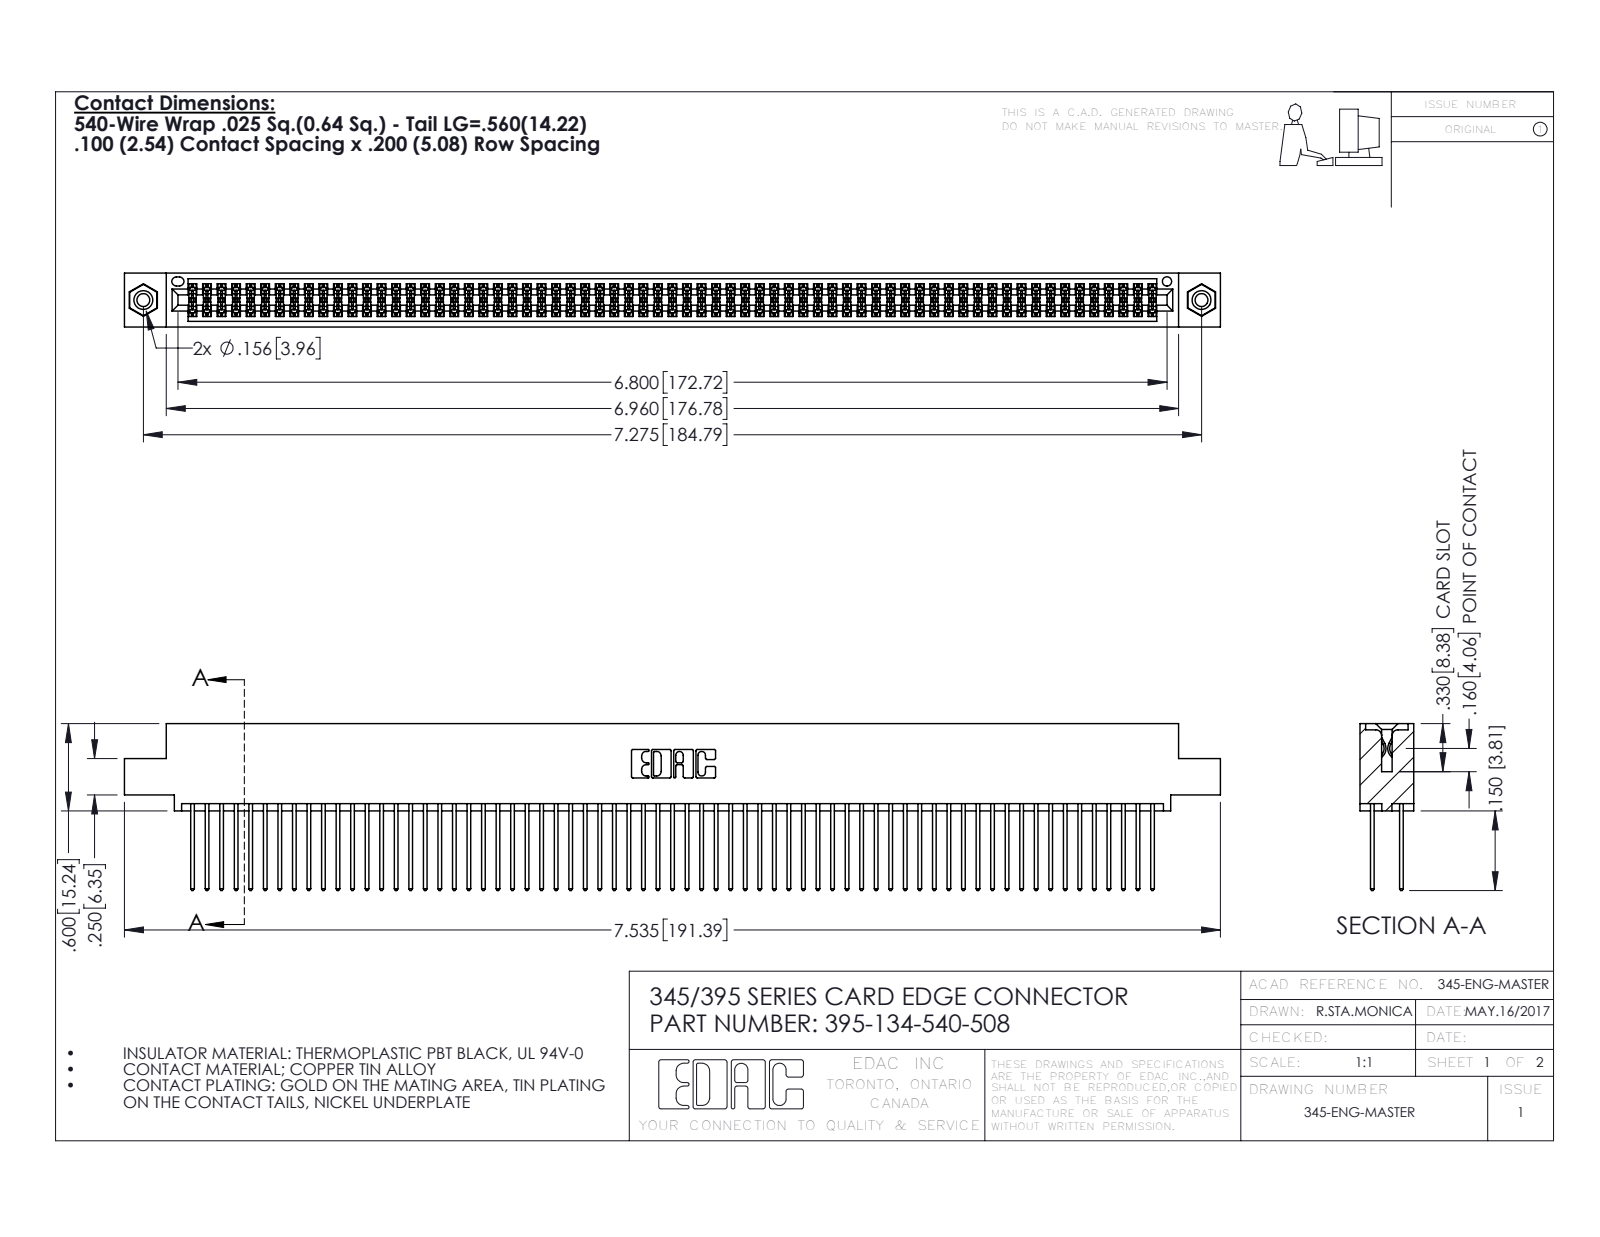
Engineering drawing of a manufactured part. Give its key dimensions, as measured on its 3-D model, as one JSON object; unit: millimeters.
{"part_name": "345 Part_0.110 Offset - 0.156 Dia-TI; 395-134-540-508; 345-292-001_345-293-140; 345-250-001_345-250-003-102", "step_written_by": "SolidWorks 2016 (CONFIG_CONTROL_DESIGN)", "units": "millimeters", "bodies": {"solids": 137, "faces": 6890, "planar": 4538, "cylindrical": 2336, "other": 16}, "overall_size": [191.4, 29.1, 9.4], "volume_mm3": 19250, "surface_area_mm2": 31410, "round_holes": [[2.3, 2], [3.2, 2], [4, 2], [1.6, 1]], "round_bosses_or_shafts": [[3.9, 2]], "partial_cylinders_radius": [[0.2, 201], [0.3, 134], [0.3, 22], [0.2, 6], [0.8, 6], [0.7, 3], [0.4, 2], [0.5, 2]], "face_to_face_distances": [1.8, 7.6, 5.1, 2.5, 6.9, 0.6, 5.7, 9.4, 4.4, 3.8], "hole_center_spacings": [6.9, 178.8, 184.8]}
